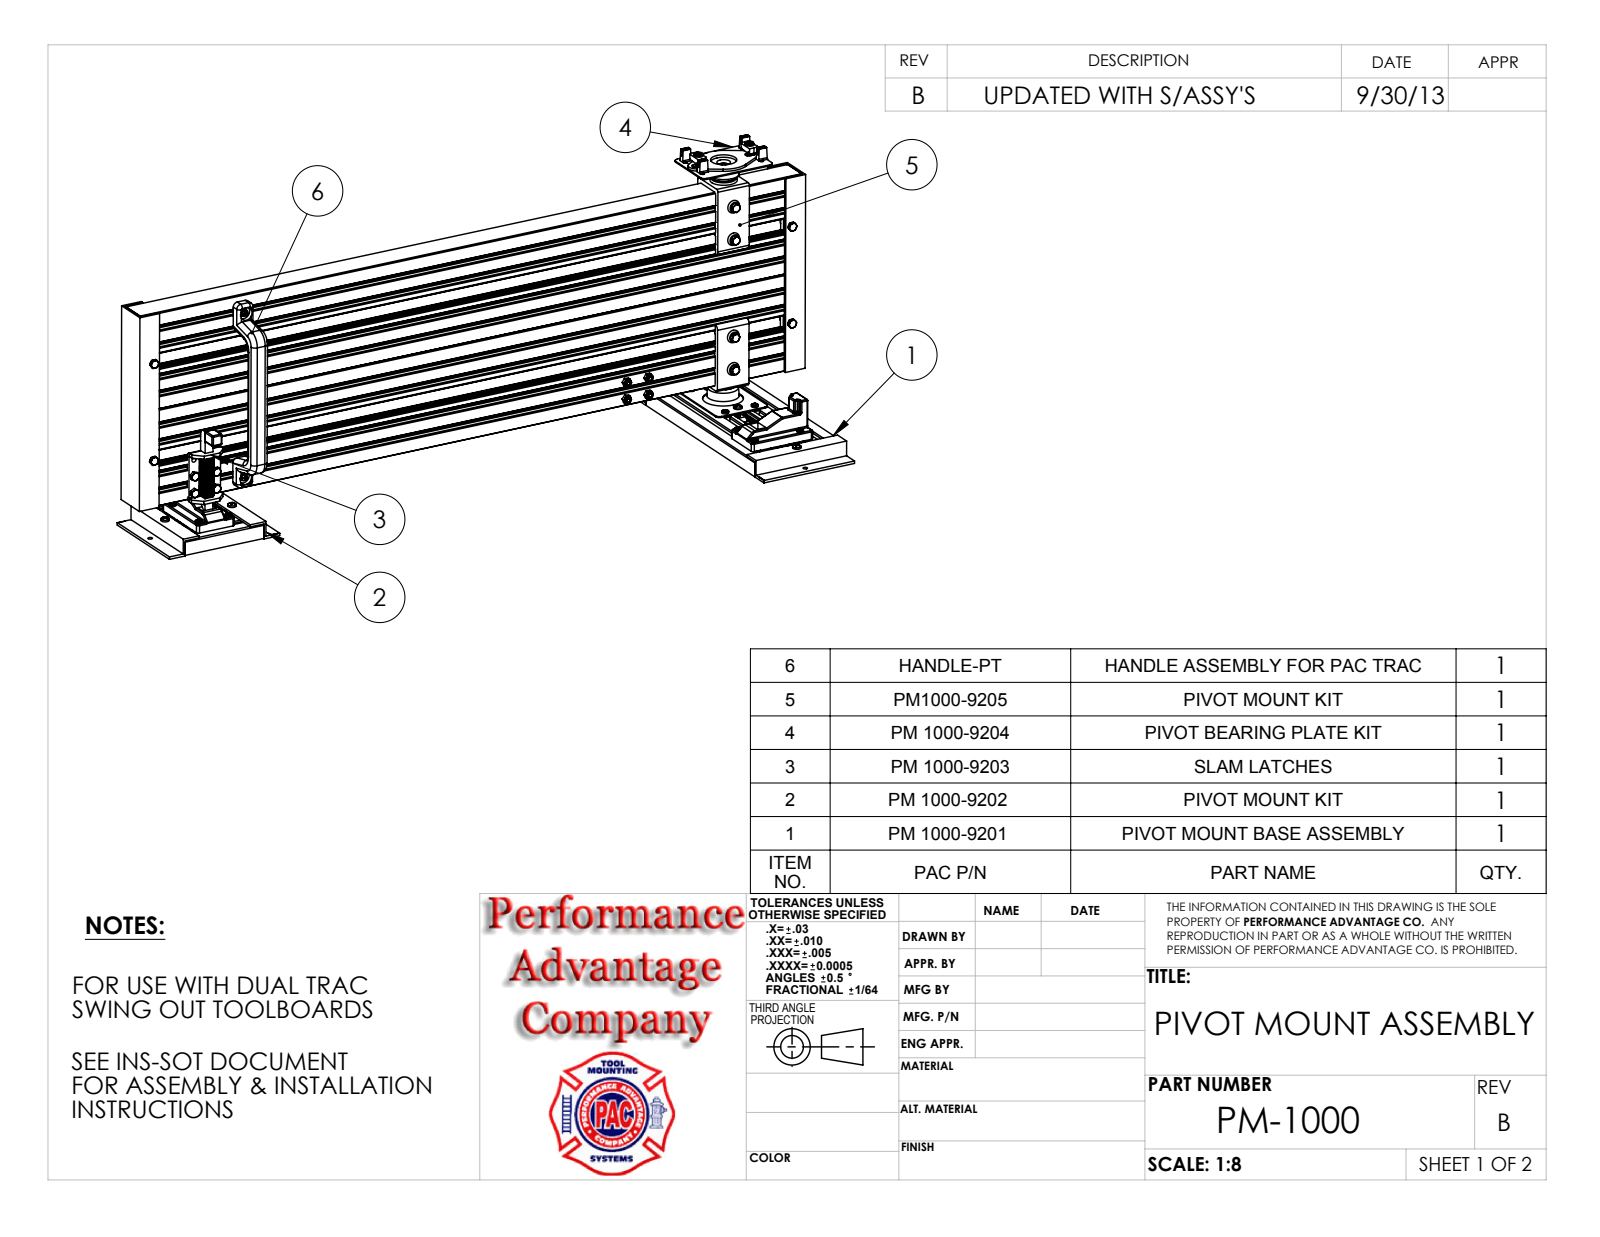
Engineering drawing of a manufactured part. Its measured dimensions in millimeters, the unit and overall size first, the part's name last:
Units: millimetres
Overall size (bounding box): 1073.2 × 387 × 355.6
Round holes (diameter × count): ⌀5.1 ×36, ⌀6.5 ×12, ⌀6.8 ×10, ⌀4.9 ×8, ⌀5.1 ×8, ⌀6.4 ×8, ⌀6.8 ×8, ⌀5.2 ×4, ⌀6.5 ×4, ⌀8.5 ×4, ⌀5.2 ×2, ⌀8.7 ×2
Round bosses / shafts (diameter × count): ⌀6.4 ×18, ⌀4.7 ×14, ⌀10.3 ×10, ⌀6.2 ×10, ⌀9.5 ×8, ⌀11.7 ×6, ⌀9.5 ×6, ⌀11.1 ×4
Partial cylindrical surfaces — rounded edges, fillets, slot ends (radius × count): R1.6 ×97, R1.6 ×71, R0.4 ×46, R2.4 ×35, R6.4 ×30, R0.4 ×28, R0.8 ×20, R11.9 ×16
Main face-to-face distances: 20.3, 2.5, 22.9, 146.1, 17.8, 40.6, 43.2, 142, 71, 38.1
Hole centre spacings: 35, 853.5, 23.8, 25.4, 43.3, 47.6, 75.3, 698.5
Volume: 5 809 000 mm³ · Surface area: 3 614 000 mm²
Bodies: 123 solids, 8667 faces (2972 planar, 1983 cylindrical, 3712 other)
Part name (STEP PRODUCT): 2023_collapsed; 7020-5_5; 7016; 2047 (+8 more)
STEP written by: SolidWorks 2014 (CONFIG_CONTROL_DESIGN)
